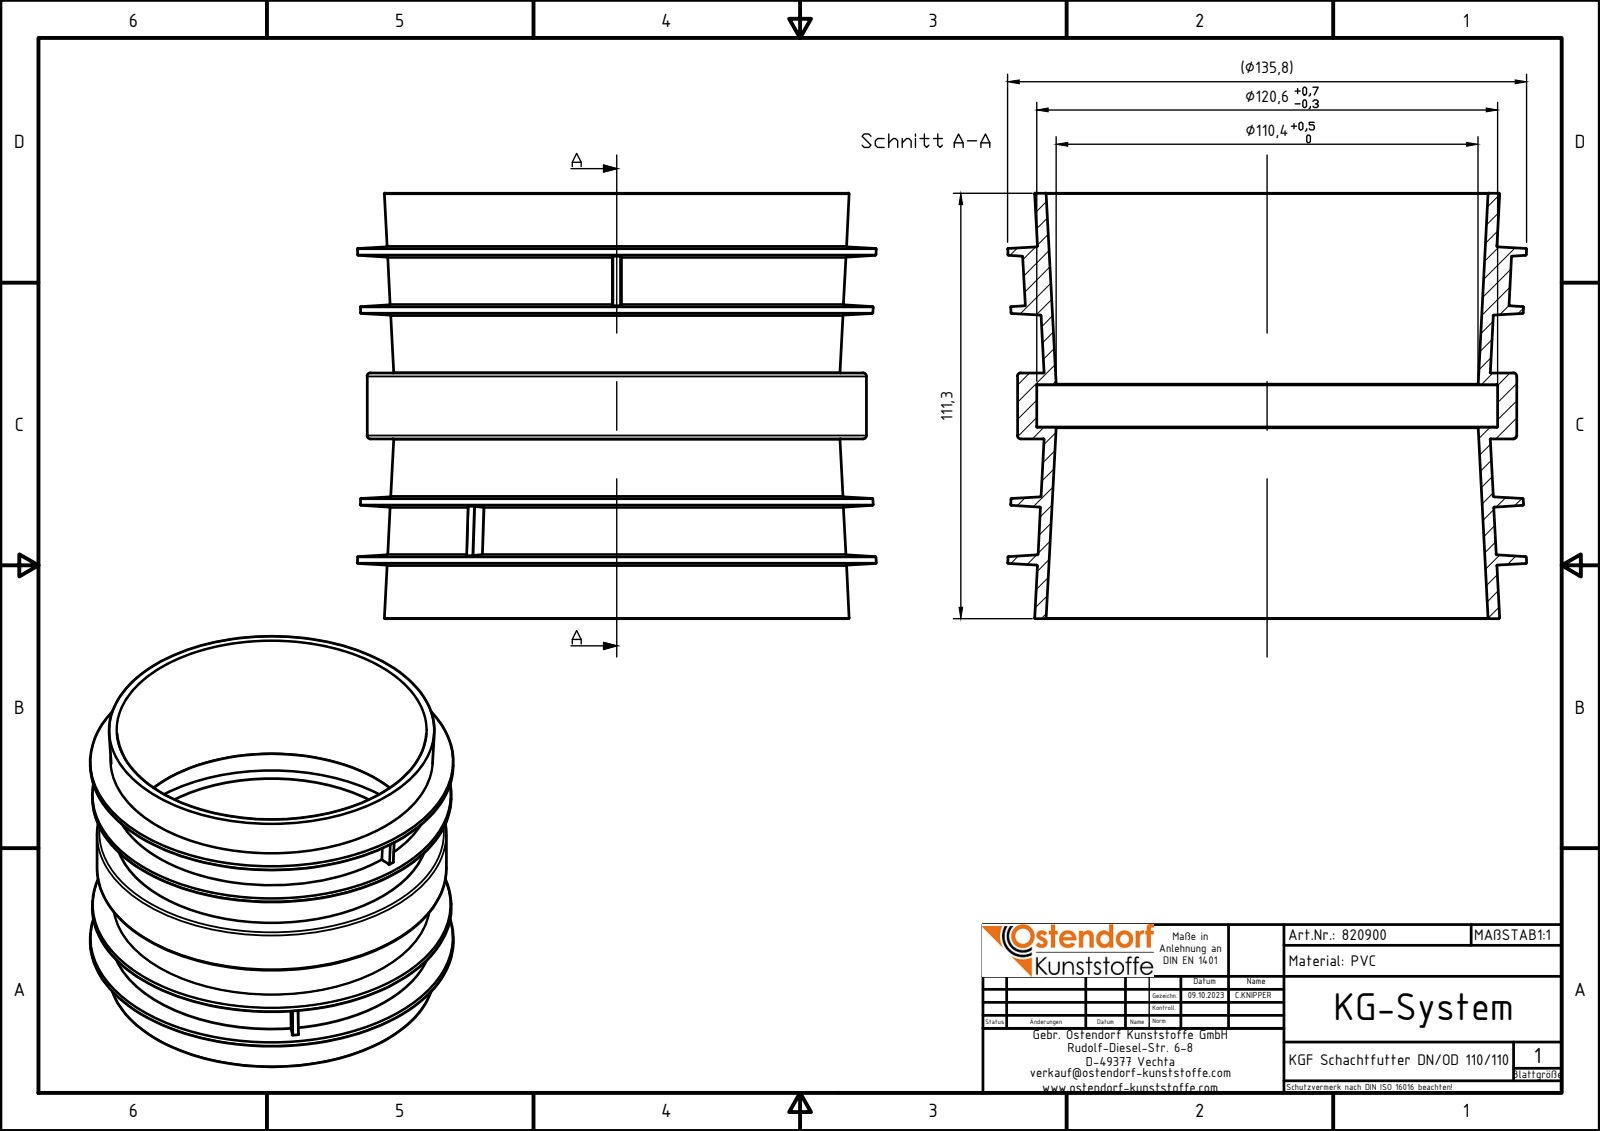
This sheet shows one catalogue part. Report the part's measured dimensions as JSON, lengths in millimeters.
{"part_name": "820900z", "step_written_by": "Autodesk Inventor 2024 (AUTOMOTIVE_DESIGN)", "units": "millimeters", "bodies": {"solids": 1, "faces": 138, "planar": 18, "cylindrical": 10, "other": 110}, "overall_size": [135.78, 135.78, 111.3], "volume_mm3": 176373, "surface_area_mm2": 116750, "round_holes": [[120.6, 1]], "round_bosses_or_shafts": [[130.6, 1]], "partial_cylinders_radius": [[0.2, 8]], "face_to_face_distances": [3, 14.2, 17.2, 47.05, 50.05, 61.25, 64.25, 11.2, 111.3, 2.2]}
